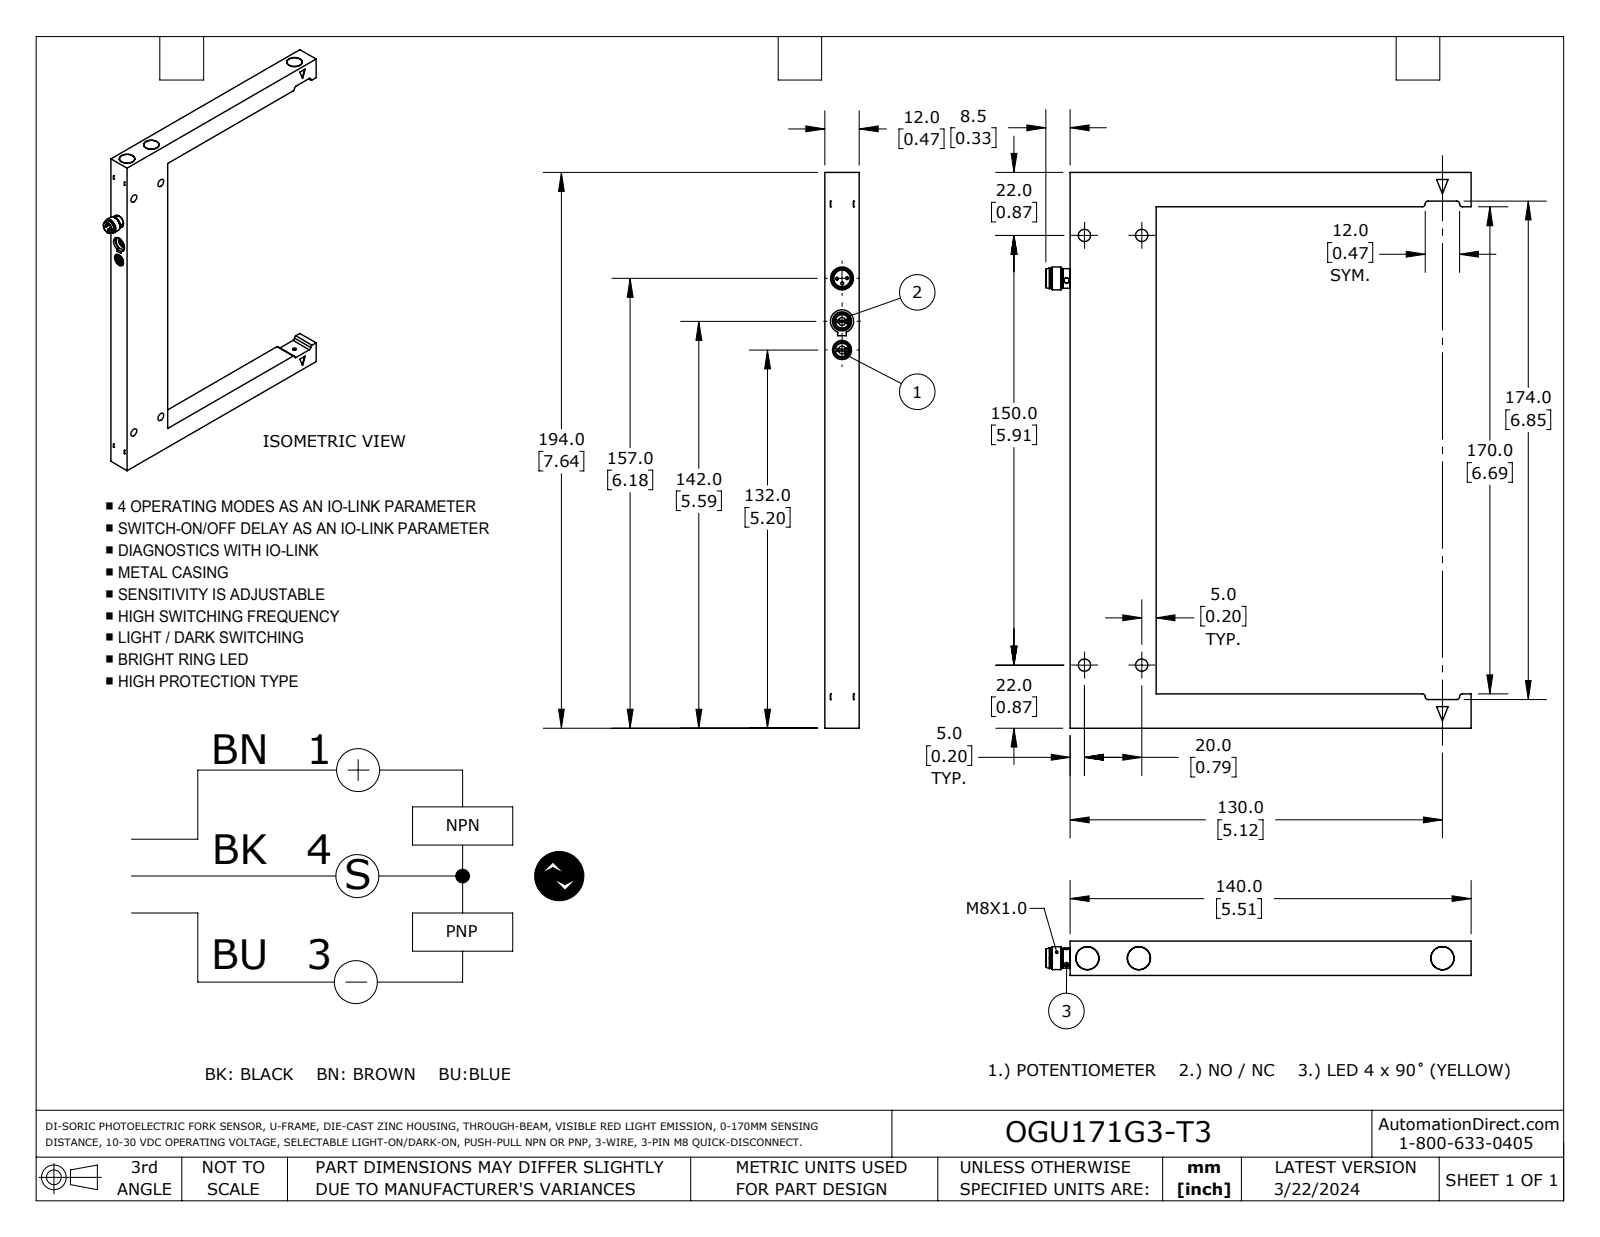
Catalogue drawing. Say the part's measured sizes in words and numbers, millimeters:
The part is named "OGU171G3-T3". Its 3-D file was written by "SolidWorks 2023 (AUTOMOTIVE_DESIGN)". It is 1 solid with 270 faces: 156 planar, 104 cylindrical and 10 other. Overall it measures 194 by 148.5 by 12 millimeters. Its volume is 99 720 cubic millimeters and its surface area 30 970 square millimeters. Round holes: 5 of diameter 8.1, 4 of diameter 4.3, 3 of diameter 1.9, 3 of diameter 5, 3 of diameter 6.7, 2 of diameter 2, 2 of diameter 3.5, 2 of diameter 4.7, 1 of diameter 2.5, 1 of diameter 2.5, 1 of diameter 2.5, 1 of diameter 5.8. Round bosses or shafts: 4 of diameter 8, 3 of diameter 7, 3 of diameter 6.6, 3 of diameter 1, 1 of diameter 8.1, 1 of diameter 7.2, 1 of diameter 6.9, 1 of diameter 6.4. Partial cylindrical surfaces (rounded edges, fillets, slot ends): 9 of radius 1, 4 of radius 0.8, 2 of radius 1.3, 2 of radius 1.5, 2 of radius 2.3, 1 of radius 0.9. The main face-to-face distances are 12, 182, 30, 194, 170, 2, 10, 1, 184, 140. The hole center spacings are 9, 18, 20, 106, 150, 151.3, 10, 15.
